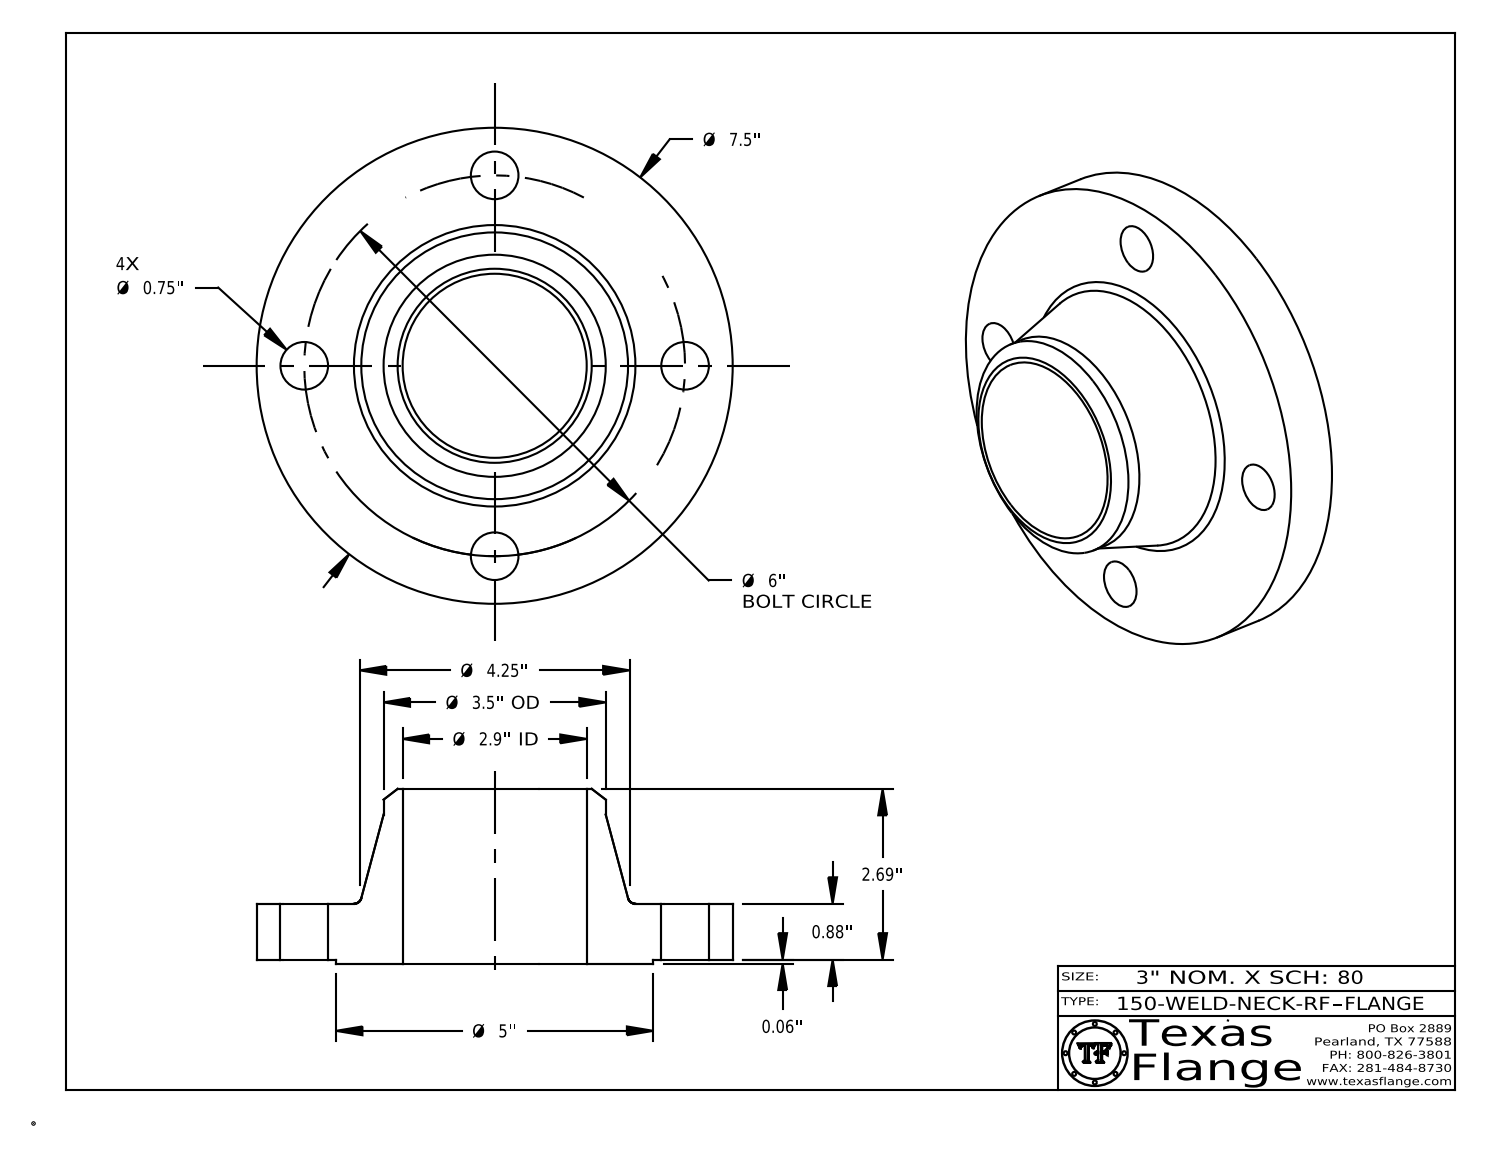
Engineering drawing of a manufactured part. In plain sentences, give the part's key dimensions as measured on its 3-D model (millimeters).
The part is named "150-WELD-NECK-RF". Its 3-D file was written by "CATIA V5 STEP AP214 (AUTOMOTIVE_DESIGN)". It is 1 solid with 411 faces: 369 planar, 36 cylindrical and 6 other. Overall it measures 190.5 by 190.5 by 69.9 millimeters. Its volume is 667 100 cubic millimeters and its surface area 92 130 square millimeters. Round holes: 4 of diameter 19.1, 1 of diameter 12.6, 1 of diameter 73.7. Round bosses or shafts: 8 of diameter 0.8, 1 of diameter 190.5, 1 of diameter 127, 1 of diameter 88.9, 1 of diameter 9.9. The main face-to-face distances are 22.4, 1.6, 24, 69.9, 68.3, 46, 23.6, 22, 0.4, 46.4. The hole center spacings are 76.2, 107.8, 58.3, 140.8, 152.4.
